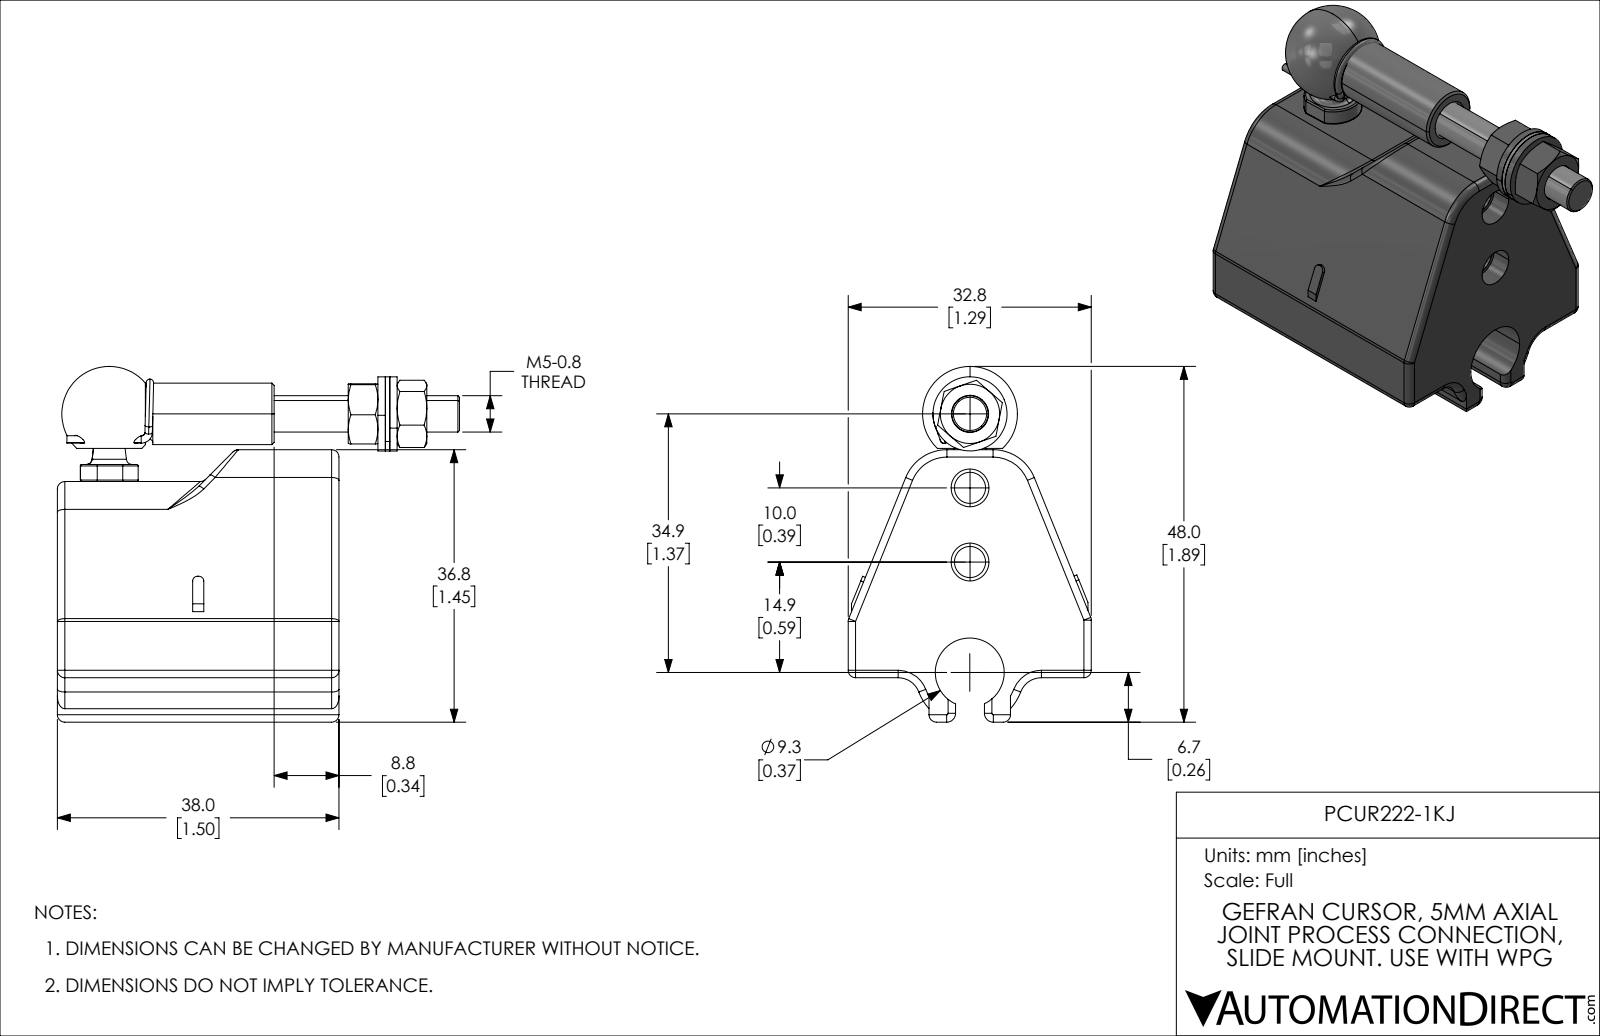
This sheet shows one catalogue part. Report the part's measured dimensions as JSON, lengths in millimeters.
{"part_name": "PCUR222-1KJ", "step_written_by": "SolidWorks 2021 (CONFIG_CONTROL_DESIGN)", "units": "millimeters", "bodies": {"solids": 11, "faces": 333, "planar": 98, "cylindrical": 117, "other": 118}, "overall_size": [54.25, 47.98, 32.8], "volume_mm3": 29549, "surface_area_mm2": 11634, "round_holes": [[4.2, 4], [5.1, 3], [1.1, 1], [5, 1], [5.3, 1], [9.3, 1]], "round_bosses_or_shafts": [[1, 2], [10, 1], [8.3, 1], [5, 1], [4.89, 1]], "partial_cylinders_radius": [[1, 28], [0.45, 8], [0.2, 4], [0.7, 4], [6, 4], [1.2, 2], [3, 2], [3.9, 1]], "face_to_face_distances": [38, 12, 25, 13, 10.4, 22.4, 32.8, 1, 10, 26.45], "hole_center_spacings": [4.91, 7.41, 9.98, 10, 14.9, 16.9, 19.98, 24.9]}
